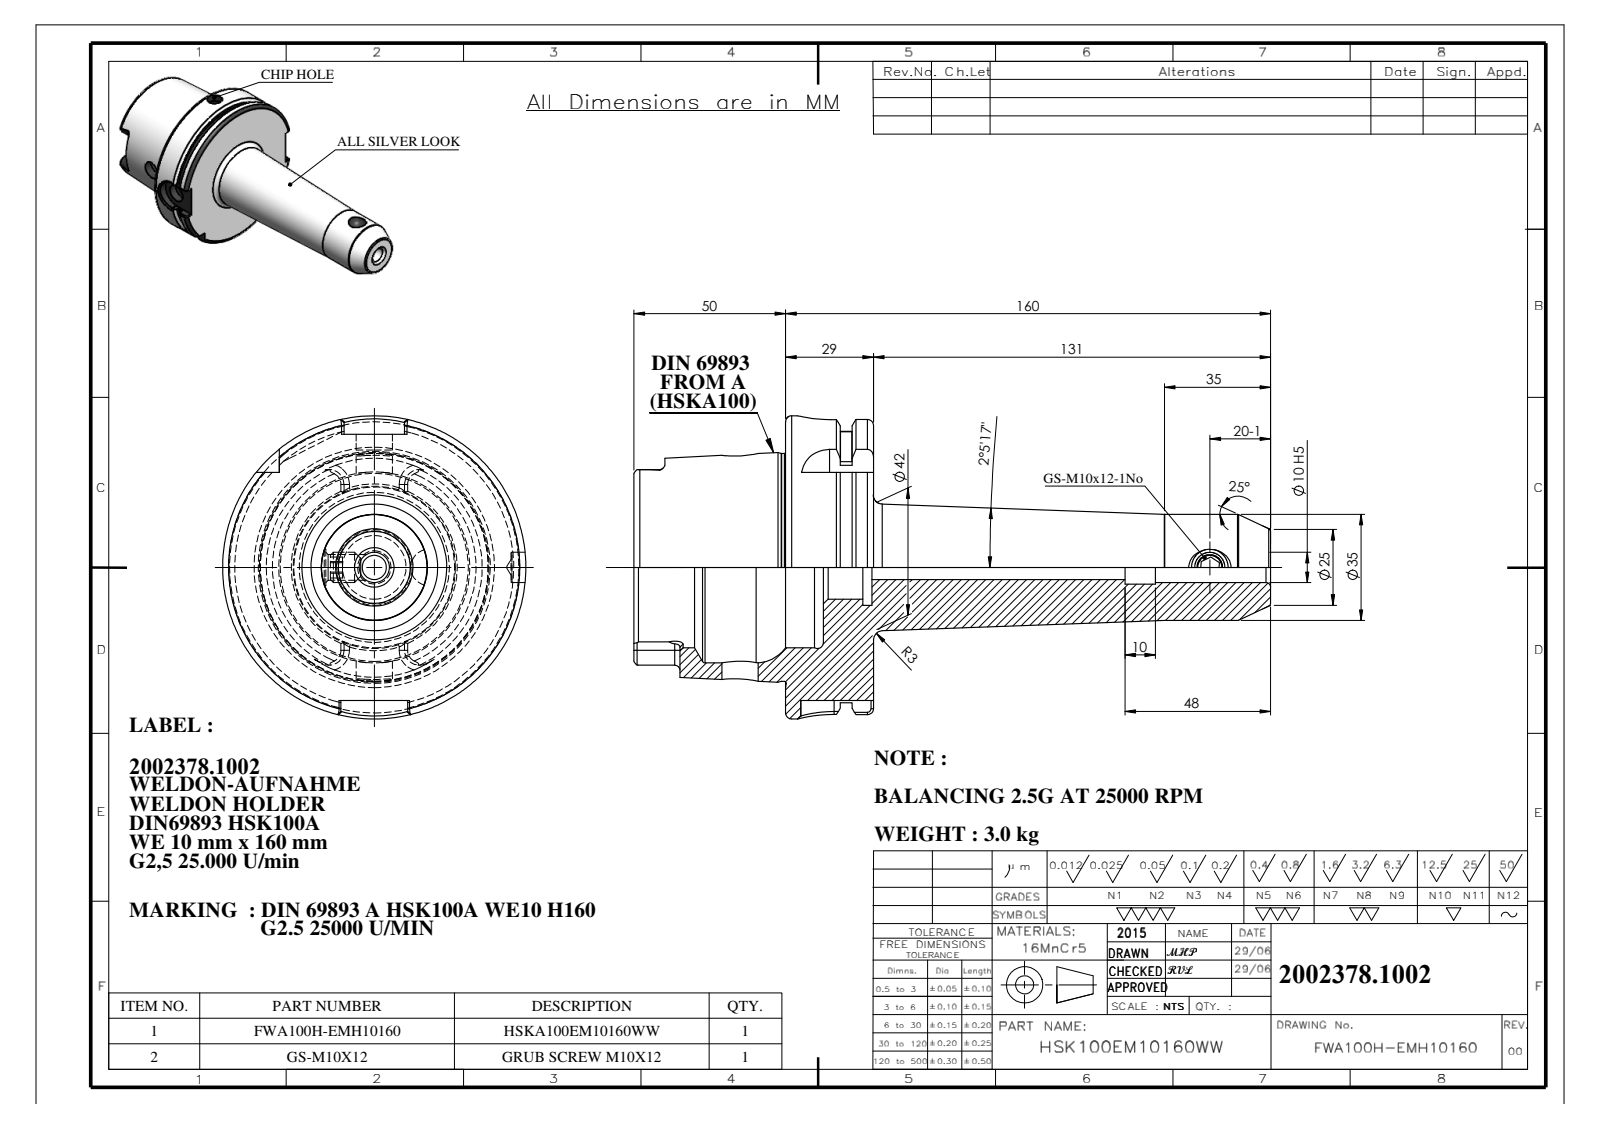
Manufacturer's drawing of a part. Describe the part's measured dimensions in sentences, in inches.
The part is named "HSKA100EM10160WW; M10X10; 91100A-WE810160". Its 3-D file was written by "SolidWorks 2018 (CONFIG_CONTROL_DESIGN)". It is 2 solids with 209 faces: 64 planar, 58 cylindrical and 87 other. Overall it measures 8.268 by 3.937 by 3.937 inches. Its volume is 23.69 cubic inches and its surface area 106 square inches. Round holes: 3 of diameter 0.472, 2 of diameter 0.394, 1 of diameter 0.315, 1 of diameter 0.335, 1 of diameter 0.433, 1 of diameter 0.827, 1 of diameter 0.984, 1 of diameter 2.087, 1 of diameter 2.48. Round bosses or shafts: 1 of diameter 3.937, 1 of diameter 3.622, 1 of diameter 2.959, 1 of diameter 1.378, 1 of diameter 0.394. Partial cylindrical surfaces (rounded edges, fillets, slot ends): 6 of radius 0.071, 4 of radius 0.192, 2 of radius 0.394, 1 of radius 0.433. The main face-to-face distances are 1.142, 0.492, 0.65, 1.969, 2.461, 3.11, 0.02, 3.091, 1.122, 0.63. The hole center spacings are 1.181, 5.236.
